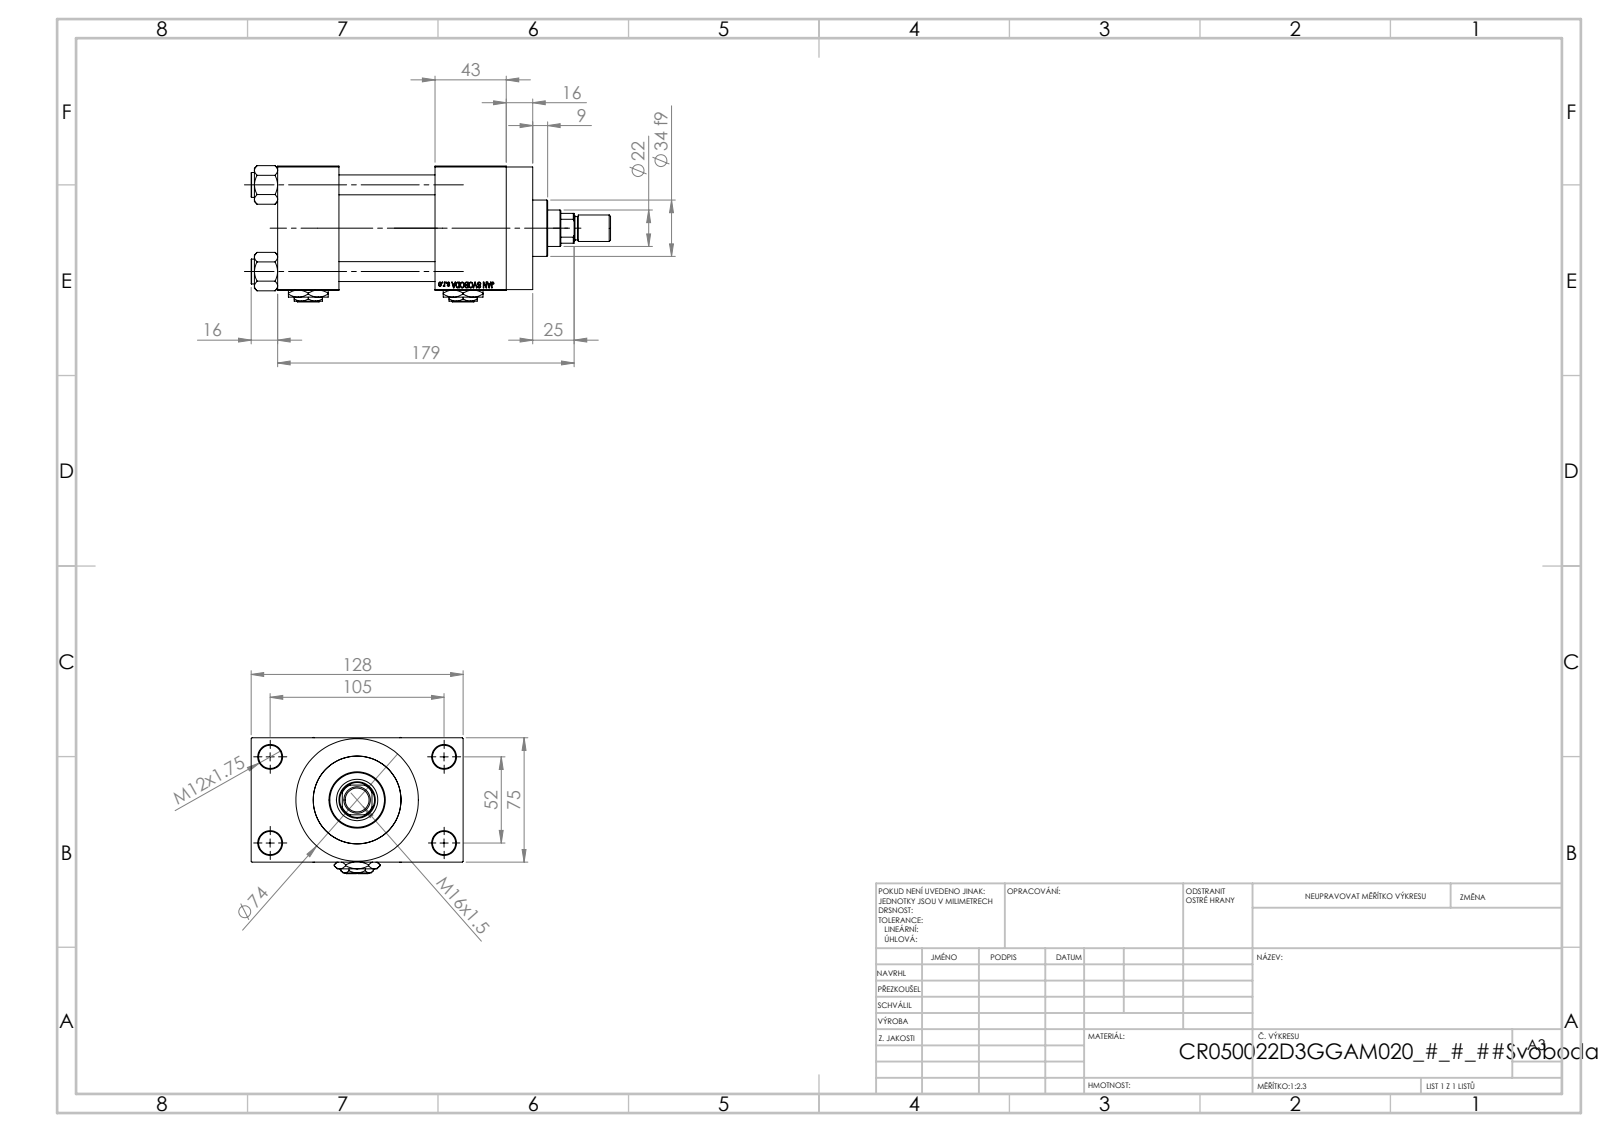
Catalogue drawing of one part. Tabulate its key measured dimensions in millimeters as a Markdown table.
| quantity | value |
| --- | --- |
| part name | V215CR_VCP_D; ROD_END_AH; V215CR_D_TYCINKA; V215_VC_A (+3 more) |
| STEP written by | SolidWorks 2019 (CONFIG_CONTROL_DESIGN) |
| units | millimeters |
| bodies | 14 solids, 1219 faces (549 planar, 104 cylindrical, 566 other) |
| overall size | 217 × 128 × 82.27 |
| volume | 806 487 mm³ |
| surface area | 170 724 mm² |
| round holes (diameter × count) | 12 × 4, 14 × 4, 7 × 2, 20.96 × 2, 30 × 2, 10.5 × 1, 22 × 1, 25 × 1, 41 × 1, 50 × 1, 53 × 1 |
| round bosses / shafts (diameter × count) | 15 × 4, 74 × 1, 56 × 1, 34 × 1, 16 × 1, 14 × 1 |
| partial cylindrical surfaces (radius × count) | 10.5 × 1 |
| main face-to-face distances | 75, 58, 37, 95, 26.5, 101.5, 101, 138, 43, 16 |
| hole center spacings | 26.35, 36.98, 52.3, 58.43, 58.59, 78.65, 94.37, 52 |
